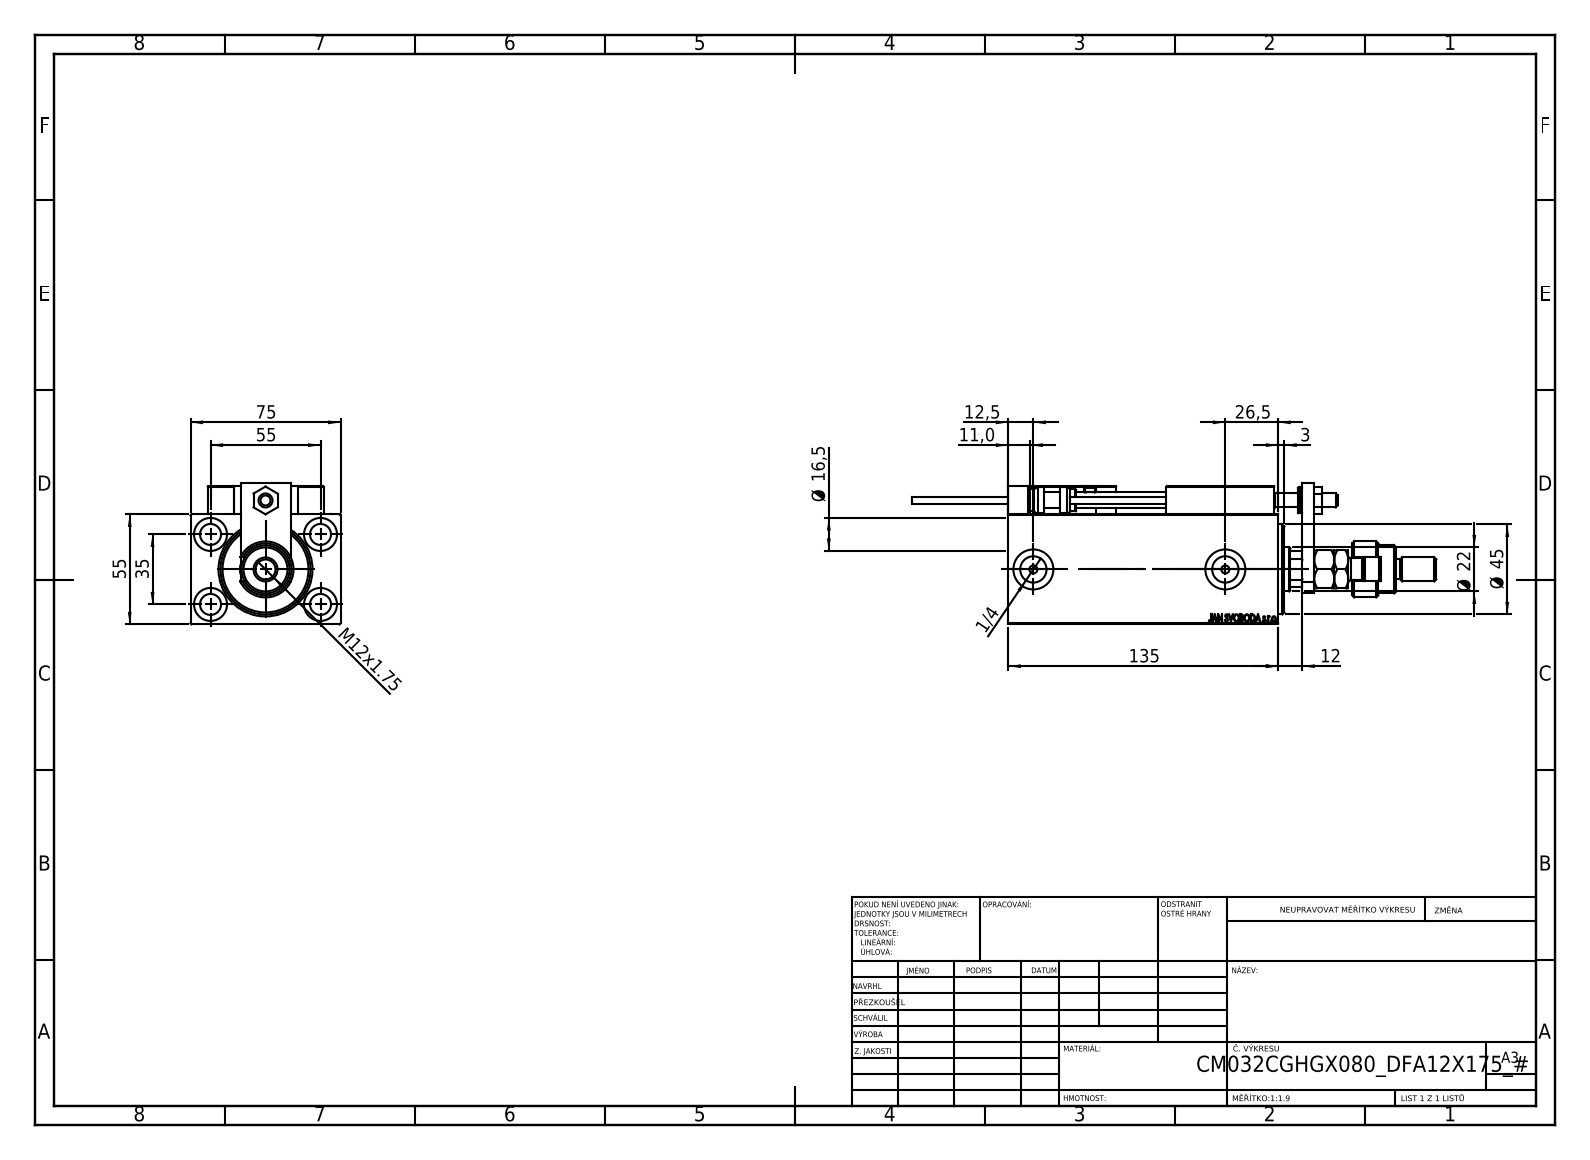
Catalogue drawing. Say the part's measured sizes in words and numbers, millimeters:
The part is named "SWITCH DIM B,W; ALLEN BOLT D5; V450CM_VC_B; Block (+7 more)". Its 3-D file was written by "SolidWorks 2019 (CONFIG_CONTROL_DESIGN)". It is 25 solids with 1367 faces: 588 planar, 201 cylindrical and 578 other. Overall it measures 262 by 75 by 70.5 millimeters. Its volume is 535 346 cubic millimeters and its surface area 126 753 square millimeters. Round holes: 6 of diameter 4, 5 of diameter 8, 5 of diameter 10.5, 5 of diameter 16.5, 4 of diameter 3.2, 2 of diameter 5, 2 of diameter 13.16, 2 of diameter 20, 1 of diameter 7, 1 of diameter 22, 1 of diameter 25.5, 1 of diameter 32. Round bosses or shafts: 2 of diameter 11, 2 of diameter 5, 2 of diameter 3.8, 1 of diameter 28, 1 of diameter 24, 1 of diameter 18, 1 of diameter 13, 1 of diameter 12. Partial cylindrical surfaces (rounded edges, fillets, slot ends): 30 of radius 0.3, 2 of radius 3, 1 of radius 9.75, 1 of radius 10.5. The main face-to-face distances are 55, 75, 14, 12, 10, 25, 69, 18, 7, 6. The hole center spacings are 32.6, 11.37, 20, 29.59, 29.69, 32.33, 35, 36.06.
